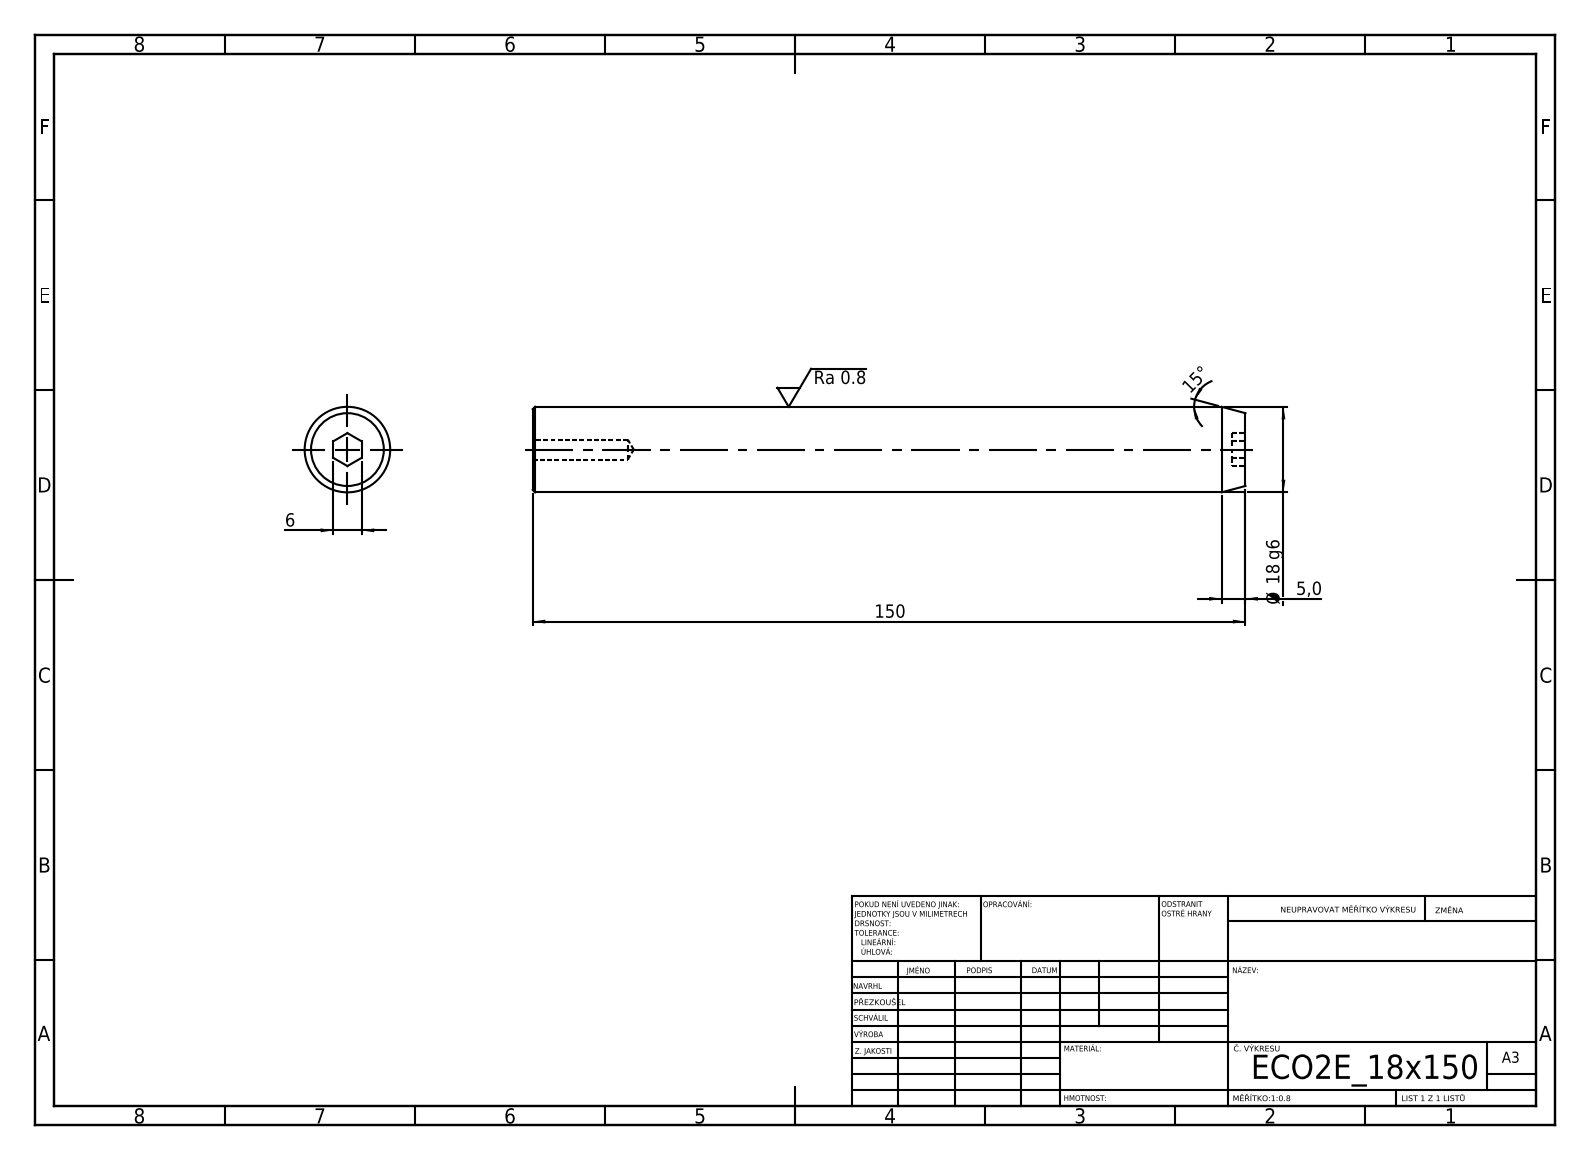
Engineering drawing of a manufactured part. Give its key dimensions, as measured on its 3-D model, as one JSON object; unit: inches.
{"step_written_by": "SolidWorks 2019 (CONFIG_CONTROL_DESIGN)", "units": "inches", "bodies": {"solids": 1, "faces": 19, "planar": 9, "cylindrical": 4, "other": 6}, "overall_size": [5.906, 0.709, 0.709], "volume_in3": 2.295, "surface_area_in2": 14.29, "round_holes": [[0.165, 1]], "round_bosses_or_shafts": [[0.709, 1]], "face_to_face_distances": [5.906, 0.11, 5.795, 0.236]}
